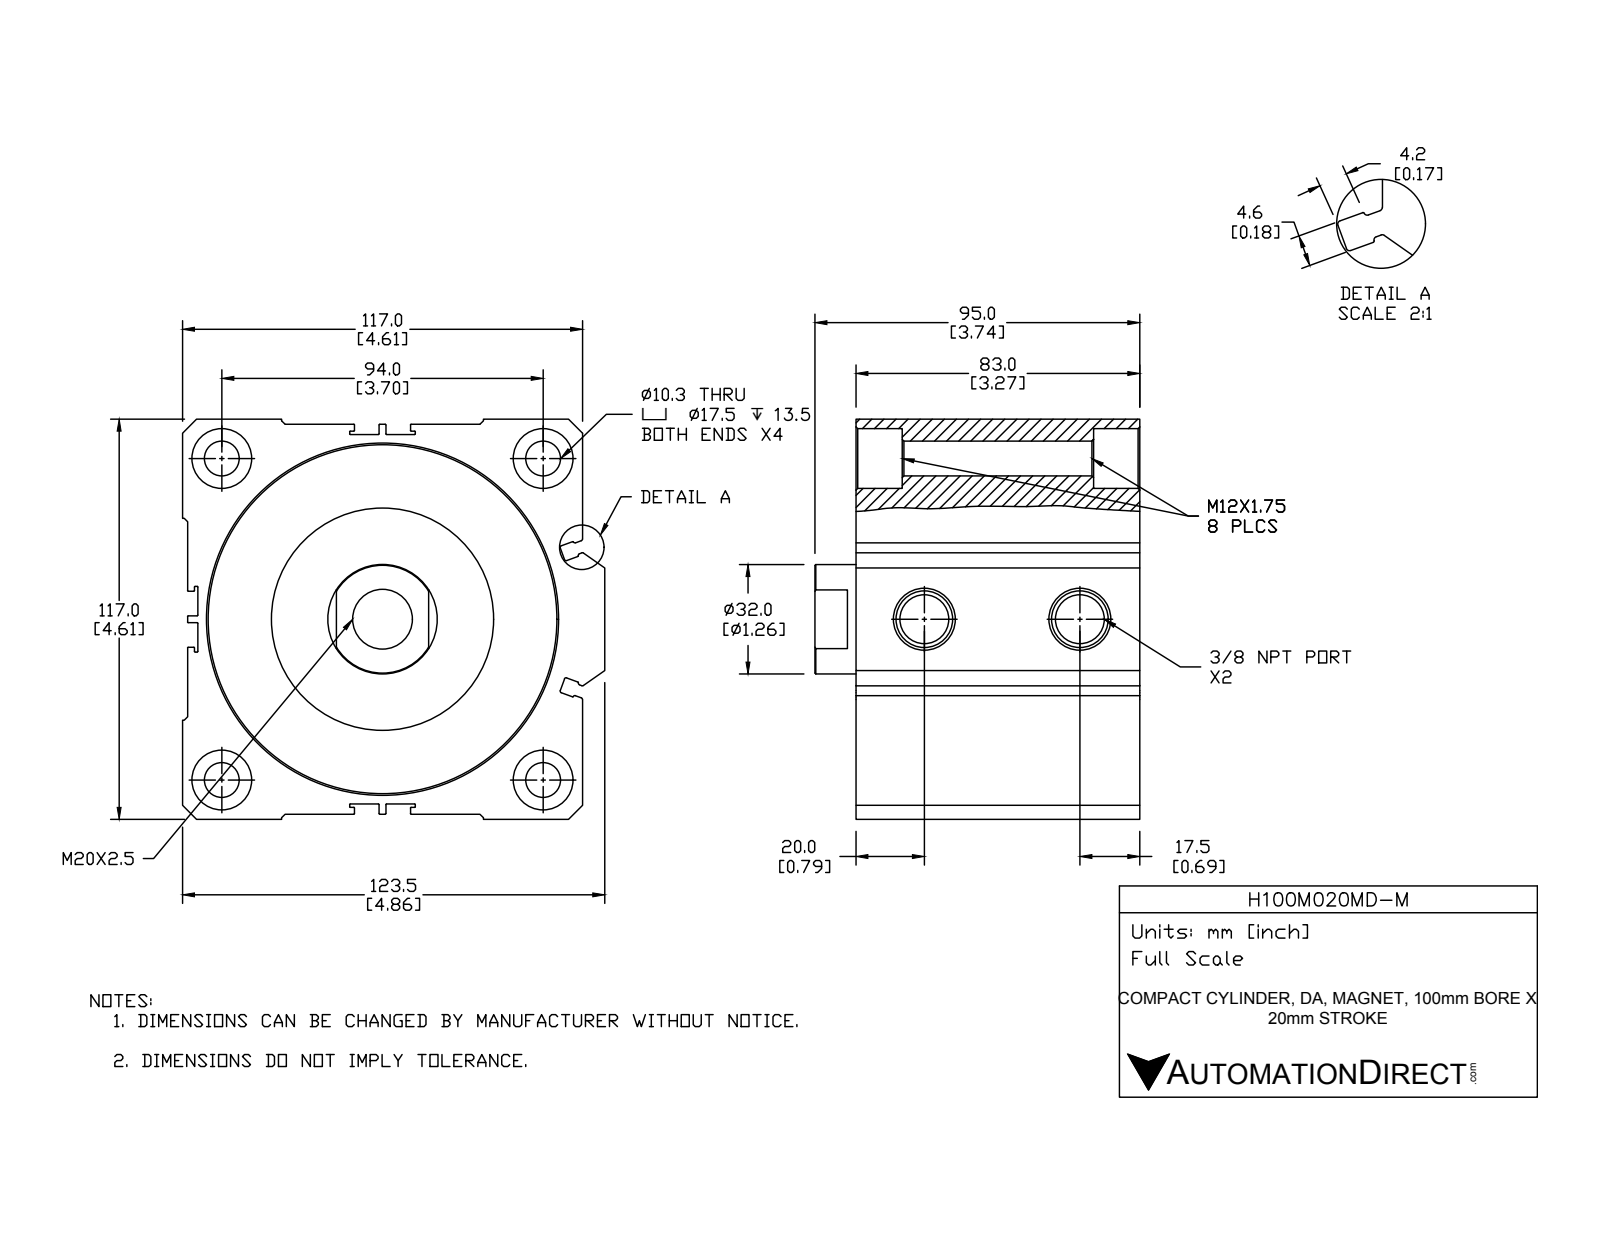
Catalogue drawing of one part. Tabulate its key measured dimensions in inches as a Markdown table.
| quantity | value |
| --- | --- |
| part name | H100M020MD-M-PISTON; H100M020MD-M-BODY; H100M020MD-M |
| STEP written by | SolidWorks 2015 (CONFIG_CONTROL_DESIGN) |
| units | inches |
| bodies | 2 solids, 261 faces (105 planar, 103 cylindrical, 53 other) |
| overall size | 4.862 × 4.606 × 3.74 |
| volume | 52.31 in³ |
| surface area | 238.9 in² |
| round holes (diameter × count) | 0.689 × 5, 0.402 × 4, 0.562 × 2, 1.26 × 1, 2.559 × 1, 3.937 × 1, 4.016 × 1 |
| round bosses / shafts (diameter × count) | 1.535 × 1 |
| partial cylindrical surfaces (radius × count) | 0.008 × 40, 0.02 × 12 |
| main face-to-face distances | 0.059, 4.547, 4.606, 1.094, 1.909, 0.815, 0.492, 1.587, 2.402, 0.472 |
| hole center spacings | 2.617, 3.701, 5.234, 1.791 |
